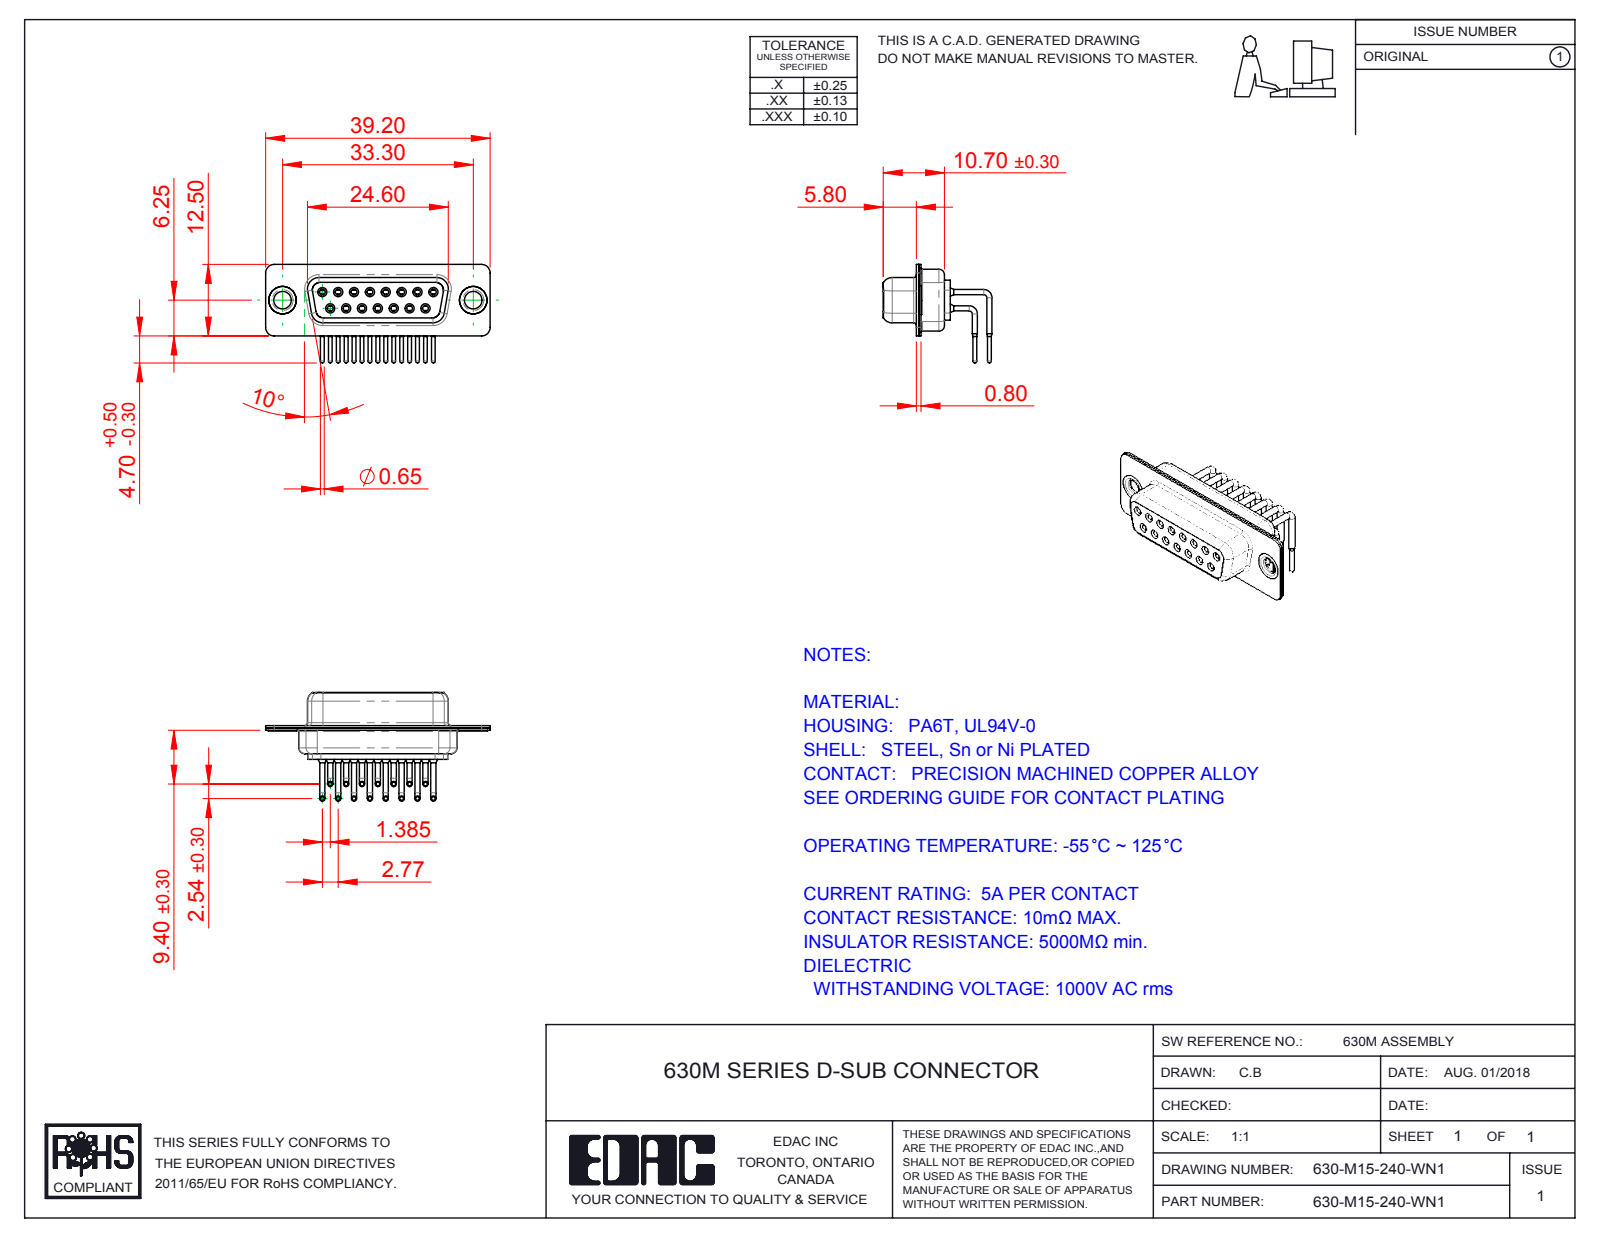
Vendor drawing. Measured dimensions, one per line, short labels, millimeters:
name: 630M Housing_15 Contacts; 630-M15-240-WN1; 630M Contact Row 1; 630M Contact Row 2 (+3 more)
written by: SolidWorks 2016 (CONFIG_CONTROL_DESIGN)
unit: mm
bodies: 20 solids, 1048 faces (292 planar, 466 cylindrical, 290 other)
size: 39.2 × 18.99 × 17.2
volume: 2 488 mm³; area: 6 404 mm²
holes: 15× ⌀1, 15× ⌀1.1, 15× ⌀1.7, 15× ⌀1.8, 15× ⌀2, 2× ⌀3.05, 2× ⌀4, 2× ⌀4.8
bosses: 30× ⌀0.9, 15× ⌀1.6, 15× ⌀1.5, 15× ⌀0.65, 2× ⌀5, 2× ⌀4.9, 2× ⌀3.55
rounds: 16× R1.5, 12× R2, 8× R1.35, 8× R1.6, 4× R0.25, 4× R0.5, 4× R0.6, 4× R0.65
face distances: 0.4, 1.45, 8.95, 6.2, 1.9, 8.5, 2.3, 0.45, 7.05, 0.85
hole spacings: 3.16, 2.77, 5.54, 8.31, 11.08, 5.03, 5.04, 7.48
